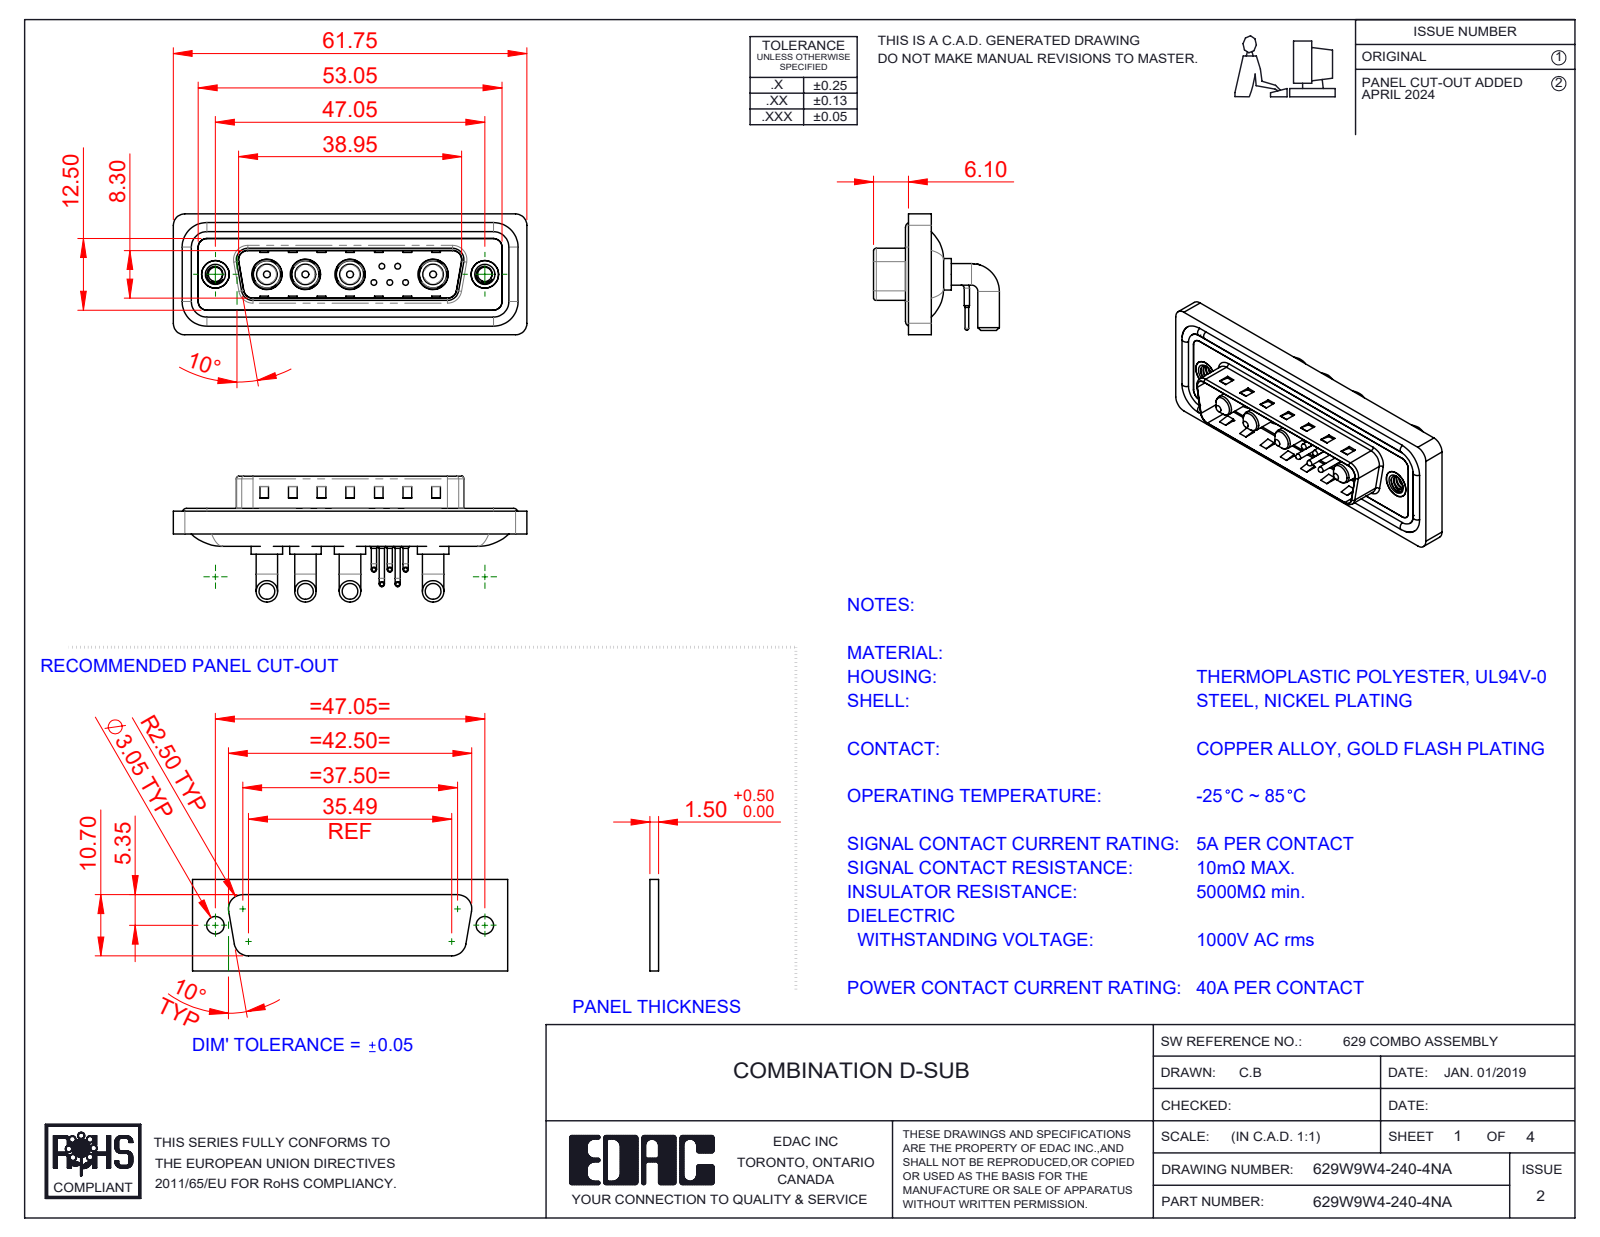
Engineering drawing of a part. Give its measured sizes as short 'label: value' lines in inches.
name: Power Pin_40A RA; 629W9W4-240-4NA; 629Combo Contact Row 2; 629Combo Shell Front_25 Contacts (+5 more)
written by: SolidWorks 2023 (CONFIG_CONTROL_DESIGN)
unit: in
bodies: 20 solids, 1199 faces (569 planar, 450 cylindrical, 180 other)
size: 2.431 × 0.865 × 0.831
volume: 0.488 in³; area: 19.46 in²
holes: 5× ⌀0.03, 5× ⌀0.063, 5× ⌀0.079, 4× ⌀0.191, 4× ⌀0.209, 2× ⌀0.098, 2× ⌀0.157, 2× ⌀0.189, 2× ⌀0.197
bosses: 10× ⌀0.035, 8× ⌀0.148, 5× ⌀0.059, 5× ⌀0.039, 5× ⌀0.026, 4× ⌀0.217, 4× ⌀0.205, 4× ⌀0.187
rounds: 18× R0.059, 18× R0.079, 8× R0.02, 8× R0.063, 5× R0.04, 4× R0.01, 4× R0.024, 4× R0.026
face distances: 0.016, 0.114, 0.031, 0.161, 0.043, 0.177, 0.083, 0.063, 0.122, 0.236
hole spacings: 0.124, 0.109, 0.198, 0.571, 0.109, 0.173, 0.174, 0.197
